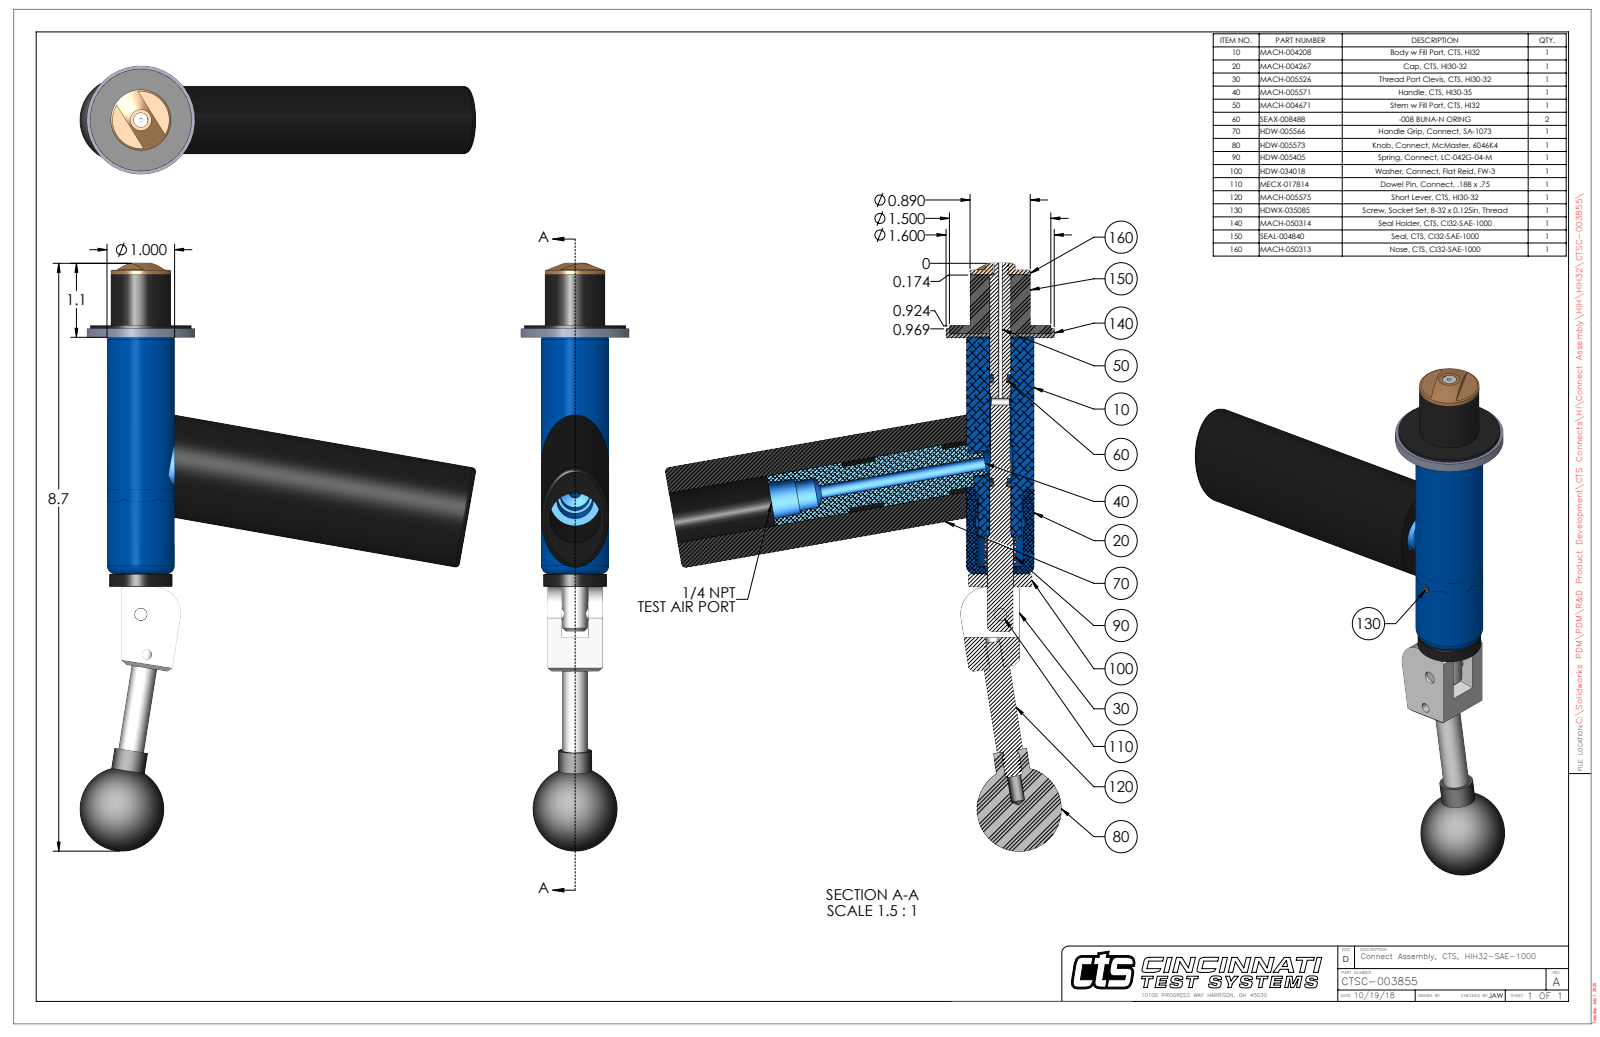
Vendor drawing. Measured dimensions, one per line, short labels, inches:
name: CTSC-003855
written by: SolidWorks 2023 (AUTOMOTIVE_DESIGN)
unit: in
bodies: 10 solids, 247 faces (82 planar, 102 cylindrical, 63 other)
size: 8.692 × 5.856 × 1.6
volume: 9.827 in³; area: 84.4 in²
holes: 2× ⌀0.201, 1× ⌀0.063, 1× ⌀0.097, 1× ⌀0.15, 1× ⌀0.187, 1× ⌀0.189, 1× ⌀0.213, 1× ⌀0.31, 1× ⌀0.314, 1× ⌀0.316, 1× ⌀0.385, 1× ⌀0.392
bosses: 2× ⌀0.25, 2× ⌀0.201, 1× ⌀1.6, 1× ⌀1, 1× ⌀0.936, 1× ⌀0.89, 1× ⌀0.75, 1× ⌀0.62
rounds: 2× R0.029, 1× R0.054, 1× R0.068, 1× R0.325, 1× R0.4, 1× R0.457
face distances: 0.06, 0.75, 0.87, 0.93, 0.21, 0.602, 0.12, 0.18, 4.608, 4.42
hole spacings: 0.599
